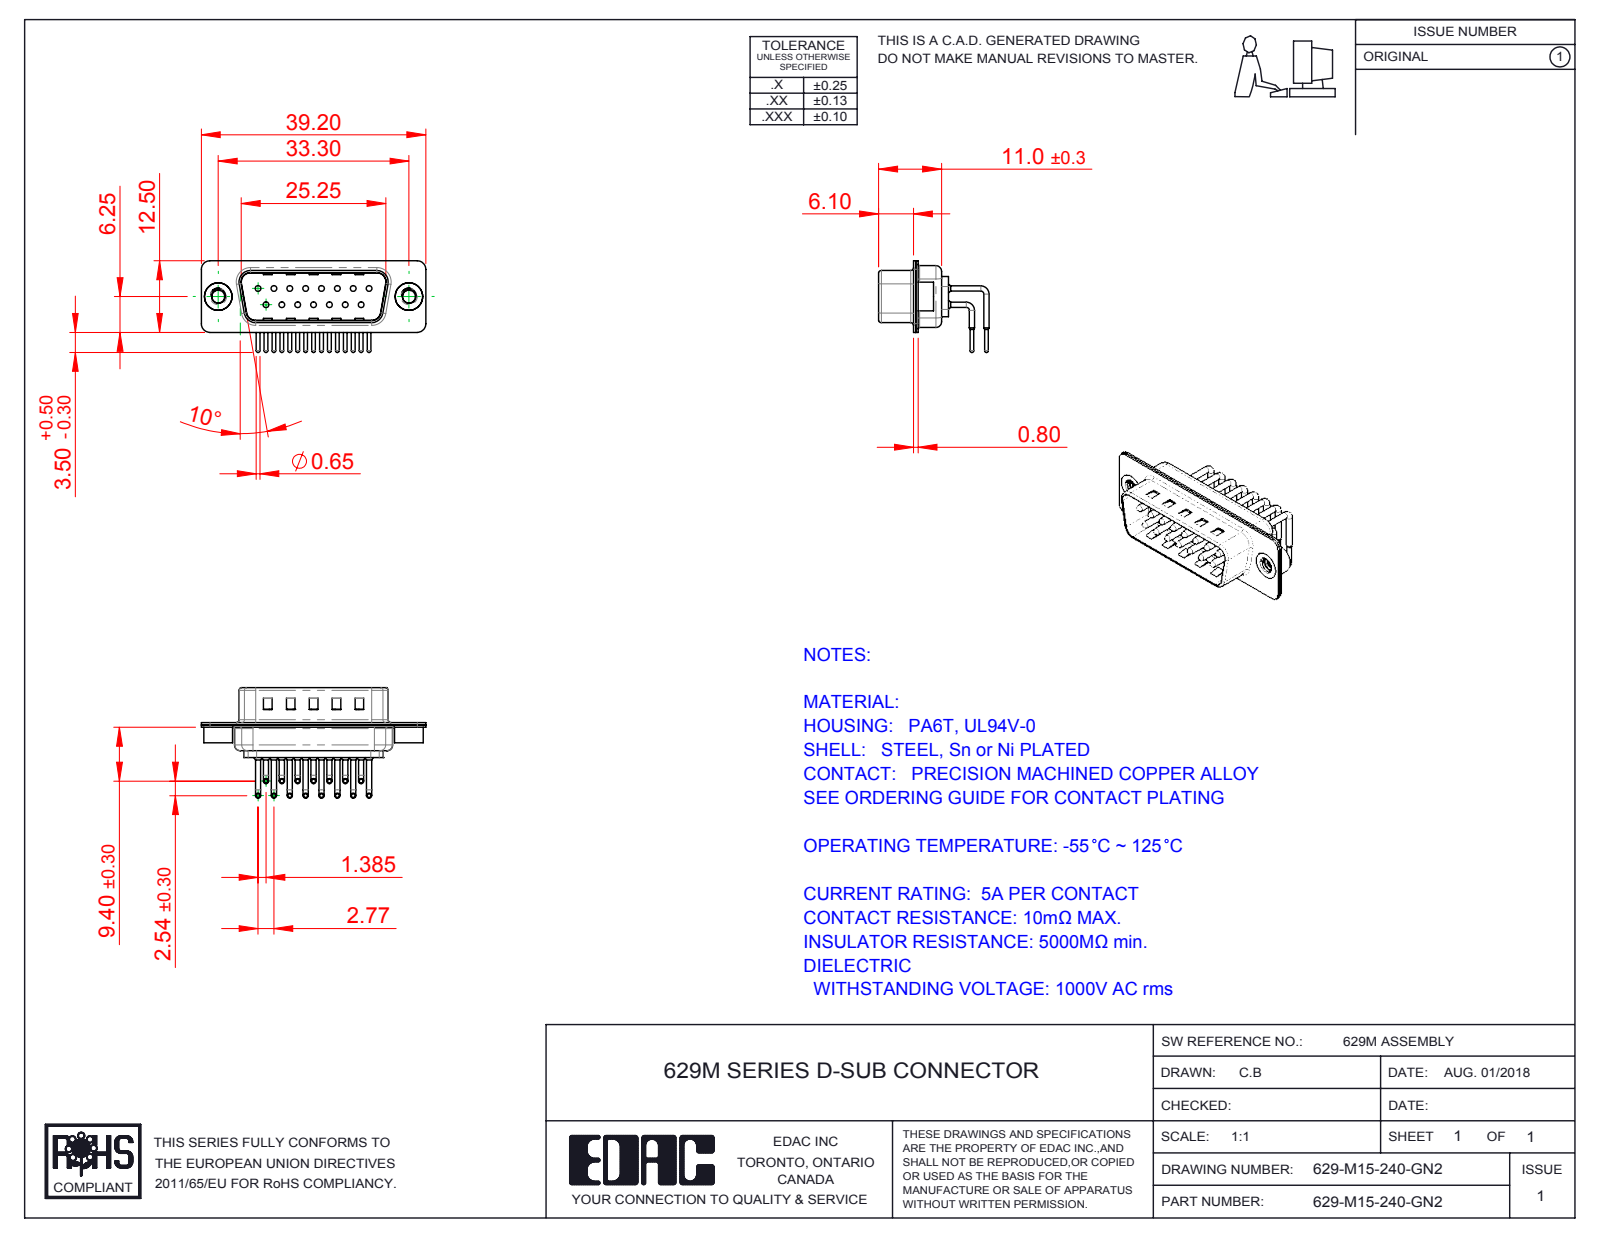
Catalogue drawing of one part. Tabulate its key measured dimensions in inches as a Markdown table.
| quantity | value |
| --- | --- |
| part name | 629M 4-40 Threaded Rivet; 629M Shell Rear_15 Contacts; 629M Contact Row 1; 629M Shell Front_15 Contacts (+3 more) |
| STEP written by | SolidWorks 2016 (CONFIG_CONTROL_DESIGN) |
| units | inches |
| bodies | 20 solids, 1990 faces (1099 planar, 673 cylindrical, 218 other) |
| overall size | 1.543 × 0.759 × 0.63 |
| volume | 0.12 in³ |
| surface area | 8.314 in² |
| round holes (diameter × count) | 0.039 × 15, 0.067 × 15, 0.079 × 15, 0.089 × 2, 0.157 × 2, 0.189 × 2 |
| round bosses / shafts (diameter × count) | 0.035 × 30, 0.059 × 15, 0.026 × 15, 0.197 × 2, 0.193 × 2 |
| partial cylindrical surfaces (radius × count) | 0.059 × 16, 0.04 × 15, 0.079 × 12, 0.02 × 8, 0.063 × 8, 0.01 × 4, 0.024 × 4, 0.026 × 4 |
| main face-to-face distances | 0.016, 0.033, 0.376, 0.343, 0.049, 0.409, 0.031, 0.059, 0.014, 0.075 |
| hole center spacings | 0.124, 0.109, 0.218, 0.327, 0.436, 0.198, 0.198, 0.294 |
